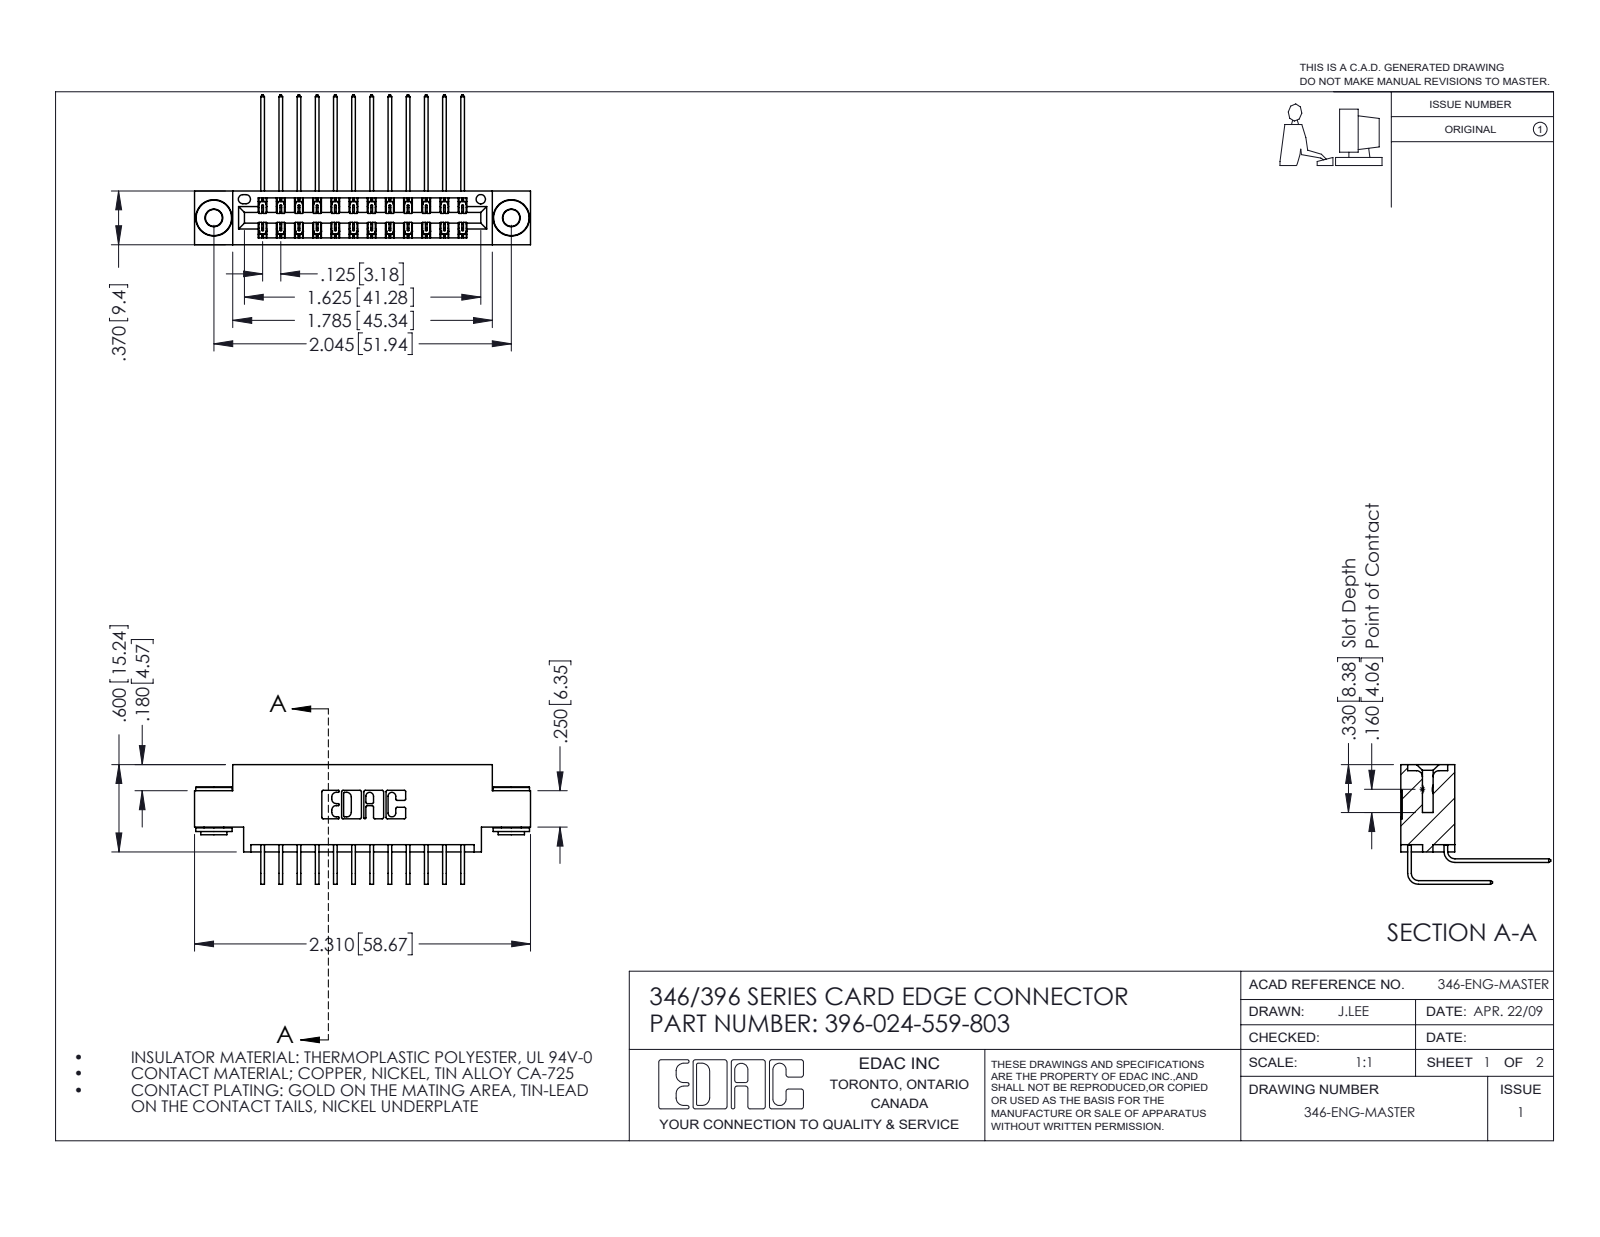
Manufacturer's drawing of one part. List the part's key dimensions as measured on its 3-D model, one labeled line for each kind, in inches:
Part name (STEP PRODUCT): 396-024-559-803; 345-292-001_558 559 Tail - 1; 346 Part_0.170 Offset - 0.156 Dia-TH; 345-292-001_559 Tail - 2 (+1 more)
STEP written by: SolidWorks 2016 (CONFIG_CONTROL_DESIGN)
Units: inches
Bodies: 27 solids, 1460 faces (978 planar, 474 cylindrical, 8 other)
Overall size (bounding box): 2.31 × 1.03 × 0.823
Volume: 0.335 in³ · Surface area: 12.61 in²
Round holes (diameter × count): ⌀0.116 ×2, ⌀0.156 ×2, ⌀0.064 ×1
Round bosses / shafts (diameter × count): ⌀0.25 ×2, ⌀0.18 ×2, ⌀0.136 ×2
Partial cylindrical surfaces — rounded edges, fillets, slot ends (radius × count): R0.006 ×36, R0.01 ×22, R0.007 ×6, R0.031 ×6, R0.026 ×3, R0.014 ×2, R0.022 ×2, R0.024 ×2
Main face-to-face distances: 0.048, 0.25, 0.37, 0.322, 0.025, 0.072, 0.298, 0.275, 0.148, 0.222
Hole centre spacings: 0.246, 1.839, 2.045
